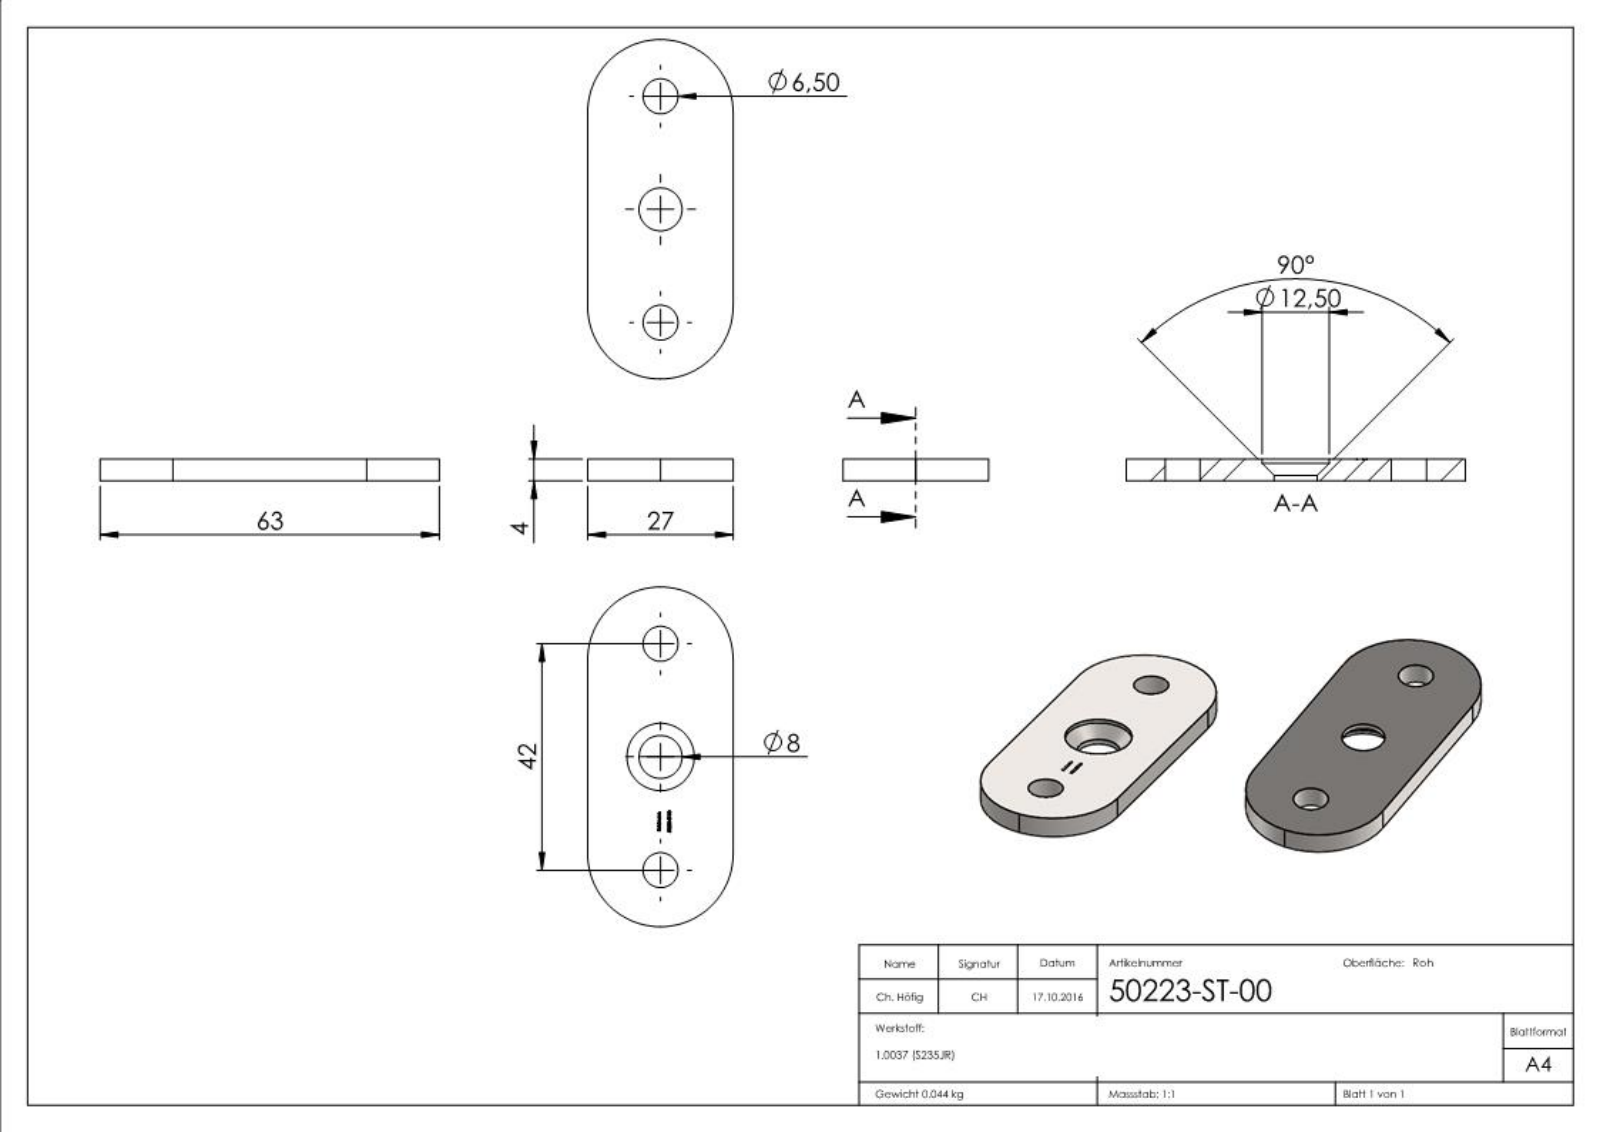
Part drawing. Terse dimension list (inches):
name: 50223-ST-00
written by: SolidWorks 2018 (CONFIG_CONTROL_DESIGN)
unit: in
bodies: 1 solid, 263 faces (123 planar, 11 cylindrical, 129 other)
size: 2.48 × 0.984 × 0.157
volume: 0.311 in³; area: 5.416 in²
holes: 2× ⌀0.256, 1× ⌀0.323, 1× ⌀0.492, 1× ⌀0.559
rounds: 2× R0.02, 2× R0.492
face distances: 0.157, 0.984, 0.02, 0.138, 0.134, 0.154, 0.073, 0.075, 0.047, 0.021
hole spacings: 0.827, 1.654
